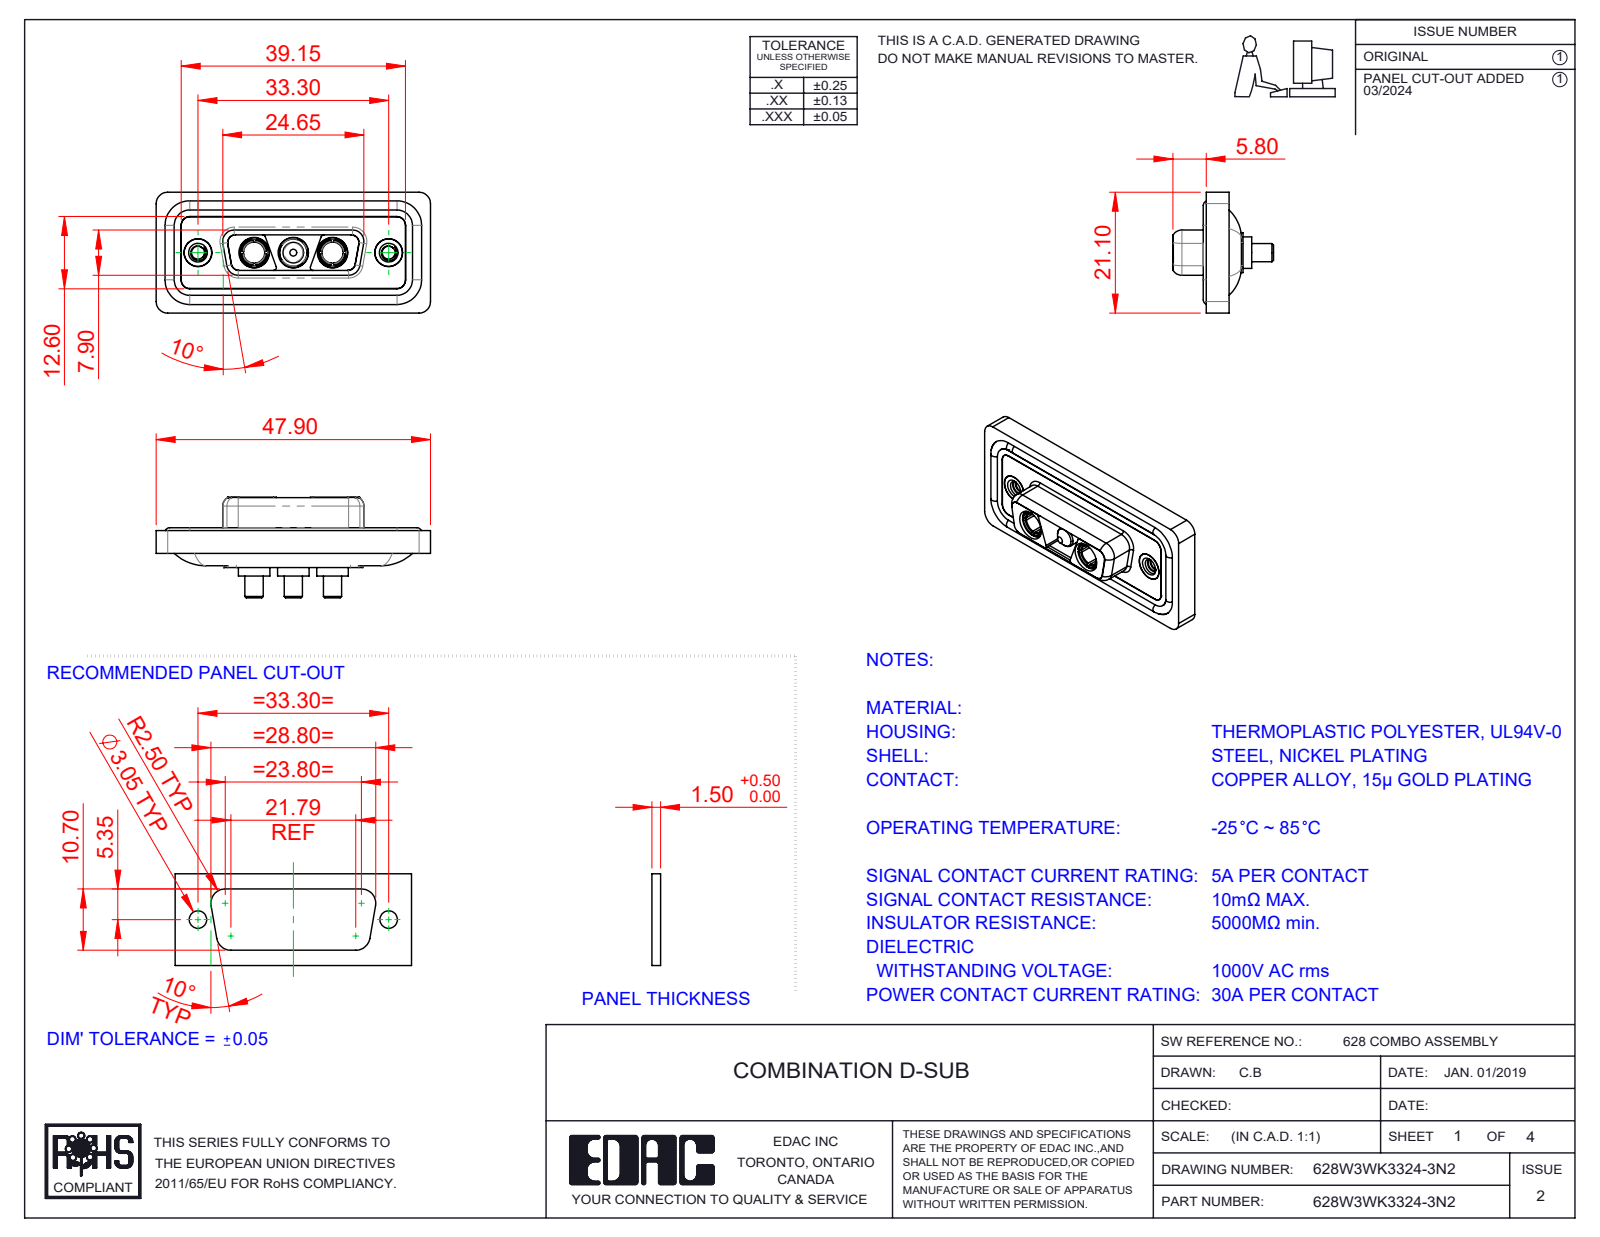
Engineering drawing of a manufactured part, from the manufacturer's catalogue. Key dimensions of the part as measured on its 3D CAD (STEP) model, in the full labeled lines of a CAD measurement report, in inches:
Part name (STEP PRODUCT): 628Combo Housing_3WK3; 628Combo Waterproof Housing_15 Contacts; Power Pin_30A S; Power Socket_30A S (+4 more)
STEP written by: SolidWorks 2023 (CONFIG_CONTROL_DESIGN)
Units: inches
Bodies: 13 solids, 583 faces (178 planar, 258 cylindrical, 147 other)
Overall size (bounding box): 1.886 × 0.831 × 0.691
Volume: 0.36 in³ · Surface area: 14.75 in²
Round holes (diameter × count): ⌀0.191 ×5, ⌀0.209 ×3, ⌀0.089 ×2, ⌀0.146 ×2, ⌀0.157 ×2, ⌀0.159 ×2, ⌀0.197 ×2
Round bosses / shafts (diameter × count): ⌀0.063 ×4, ⌀0.217 ×3, ⌀0.205 ×3, ⌀0.187 ×3, ⌀0.148 ×3, ⌀0.126 ×3, ⌀0.195 ×2, ⌀0.195 ×2
Partial cylindrical surfaces — rounded edges, fillets, slot ends (radius × count): R0.059 ×22, R0.079 ×20, R0.053 ×12, R0.02 ×8, R0.063 ×8, R0.01 ×4, R0.024 ×4, R0.026 ×4
Main face-to-face distances: 0.016, 0.063, 0.02, 0.071, 0.043, 0.114, 0.222, 0.278, 0.211, 0.059
Hole centre spacings: 0.27, 0.386, 0.656, 0.925, 0.539, 1.311
